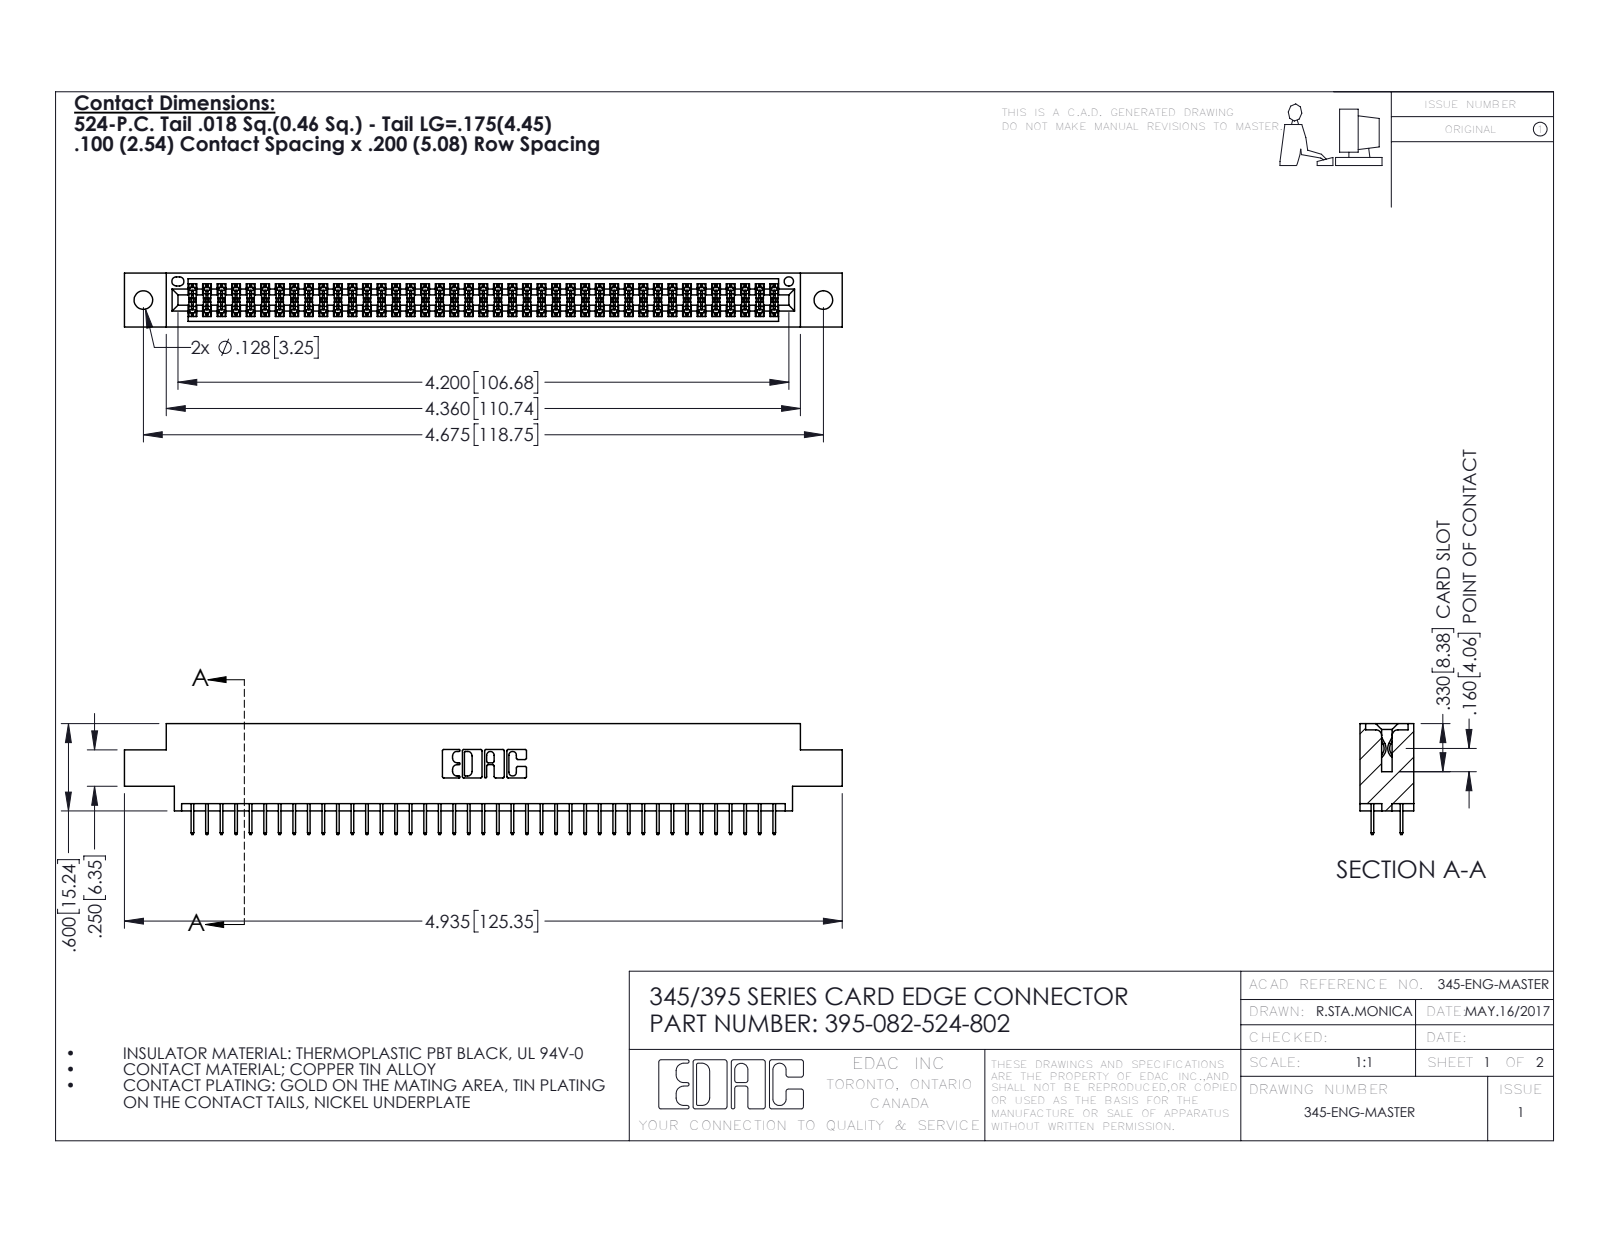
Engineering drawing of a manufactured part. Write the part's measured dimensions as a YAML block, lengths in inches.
part_name: "345-292-001_345-293-124; 395-082-524-802; 345 Part_0.170 Offset - 0.128 Dia"
step_written_by: "SolidWorks 2016 (CONFIG_CONTROL_DESIGN)"
units: inches
bodies: {solids: 83, faces: 4558, planar: 3282, cylindrical: 1276, other: 0}
overall_size: [4.935, 0.762, 0.37]
volume: 0.726
surface_area: 26.51
round_holes:
  - {diameter: 0.128, count: 2}
  - {diameter: 0.064, count: 1}
partial_cylinders:
  - {radius: 0.006, count: 123}
  - {radius: 0.01, count: 22}
  - {radius: 0.007, count: 6}
  - {radius: 0.031, count: 6}
  - {radius: 0.026, count: 3}
  - {radius: 0.014, count: 2}
  - {radius: 0.019, count: 2}
  - {radius: 0.022, count: 2}
face_to_face_distances: [0.072, 0.298, 0.37, 0.2, 0.098, 0.272, 0.025, 0.225, 0.175, 0.072]
hole_center_spacings: [0.27, 4.439, 4.675]
